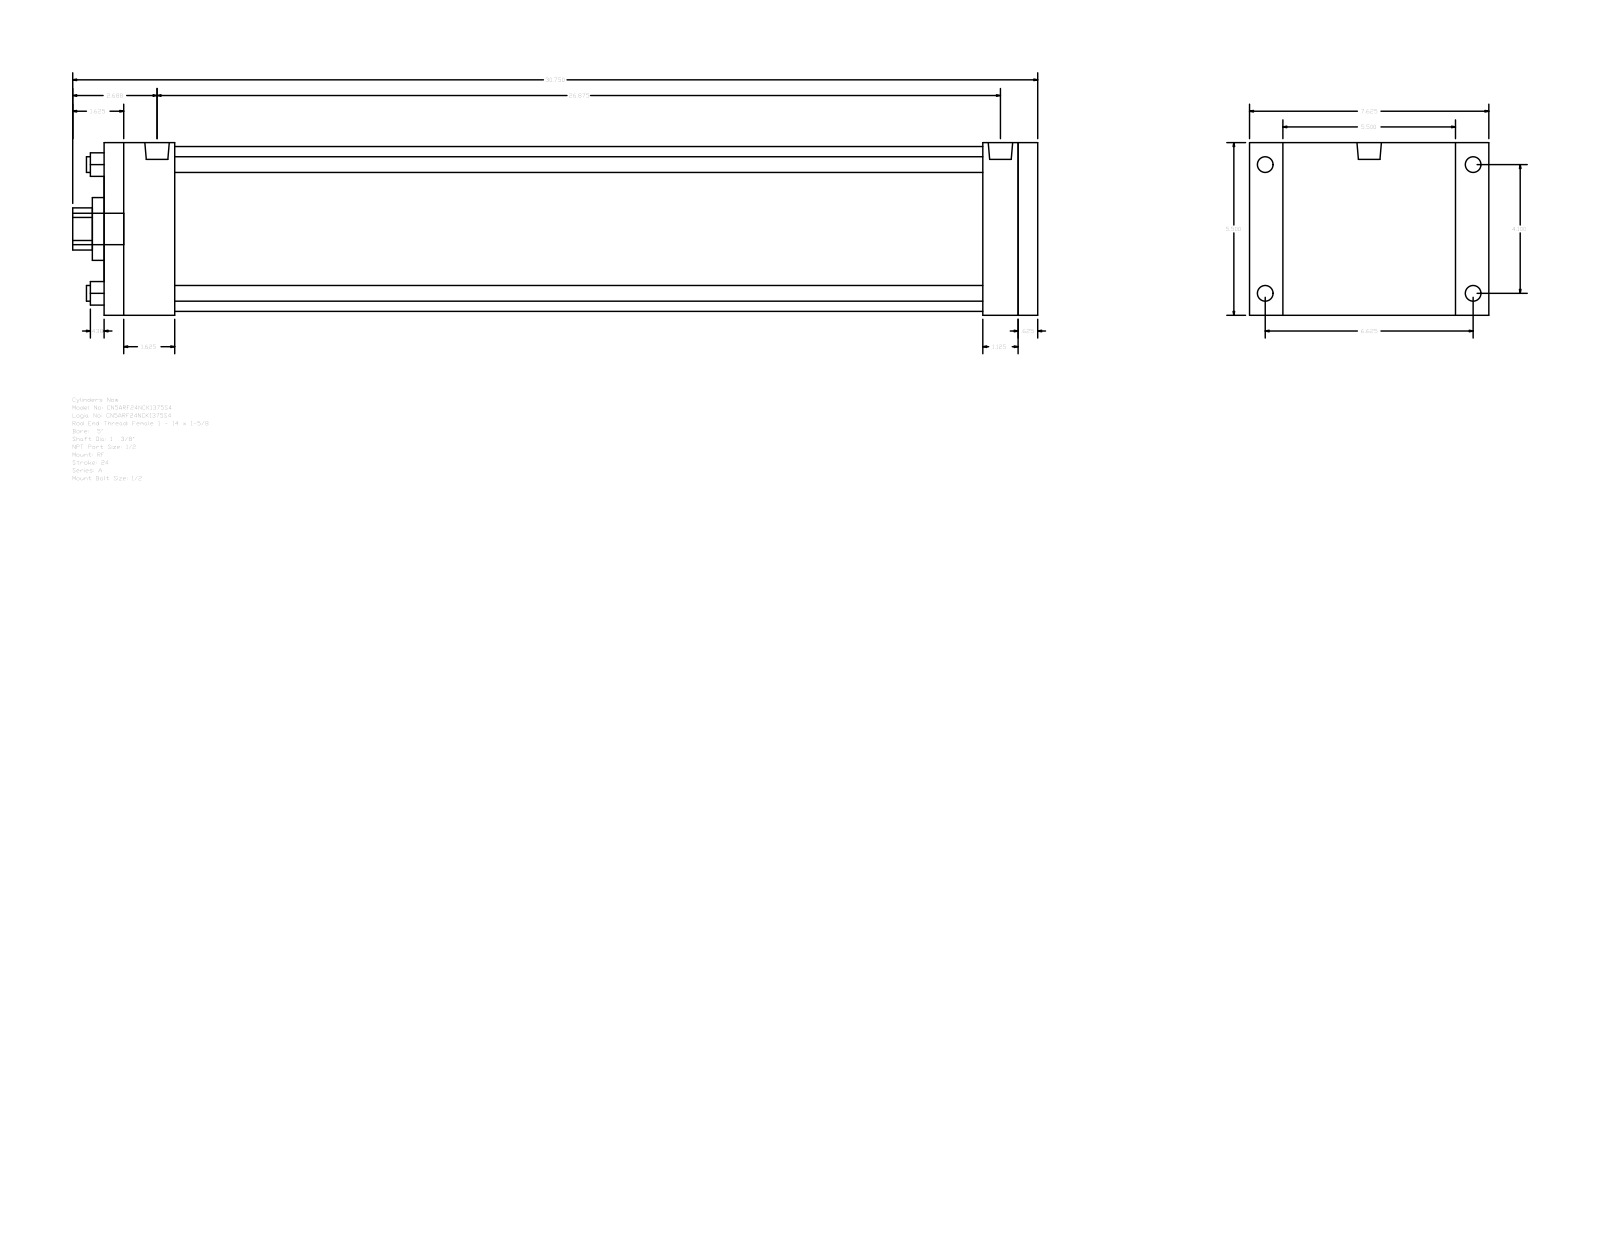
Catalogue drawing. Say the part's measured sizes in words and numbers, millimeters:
The part is named "A_RF__0500_1.375". Its 3-D file was written by "GSSL Pune (CONFIG_CONTROL_DESIGN)". It is 0 solids with 92 faces: 64 planar, 28 cylindrical and 0 other. Overall it measures 781.05 by 193.68 by 139.7 millimeters. Round holes: 4 of diameter 12.7, 1 of diameter 34.92, 1 of diameter 50.8, 1 of diameter 133.35. Round bosses or shafts: 4 of diameter 12.7, 4 of diameter 8.73, 2 of diameter 19.77, 1 of diameter 25.4. Partial cylindrical surfaces (rounded edges, fillets, slot ends): 1 of radius 17.06. The main face-to-face distances are 139.7, 755.65, 15.88, 739.77, 28.57, 57.15, 682.62, 698.5, 711.2, 654.05. The hole center spacings are 73.64, 104.14, 147.28.
